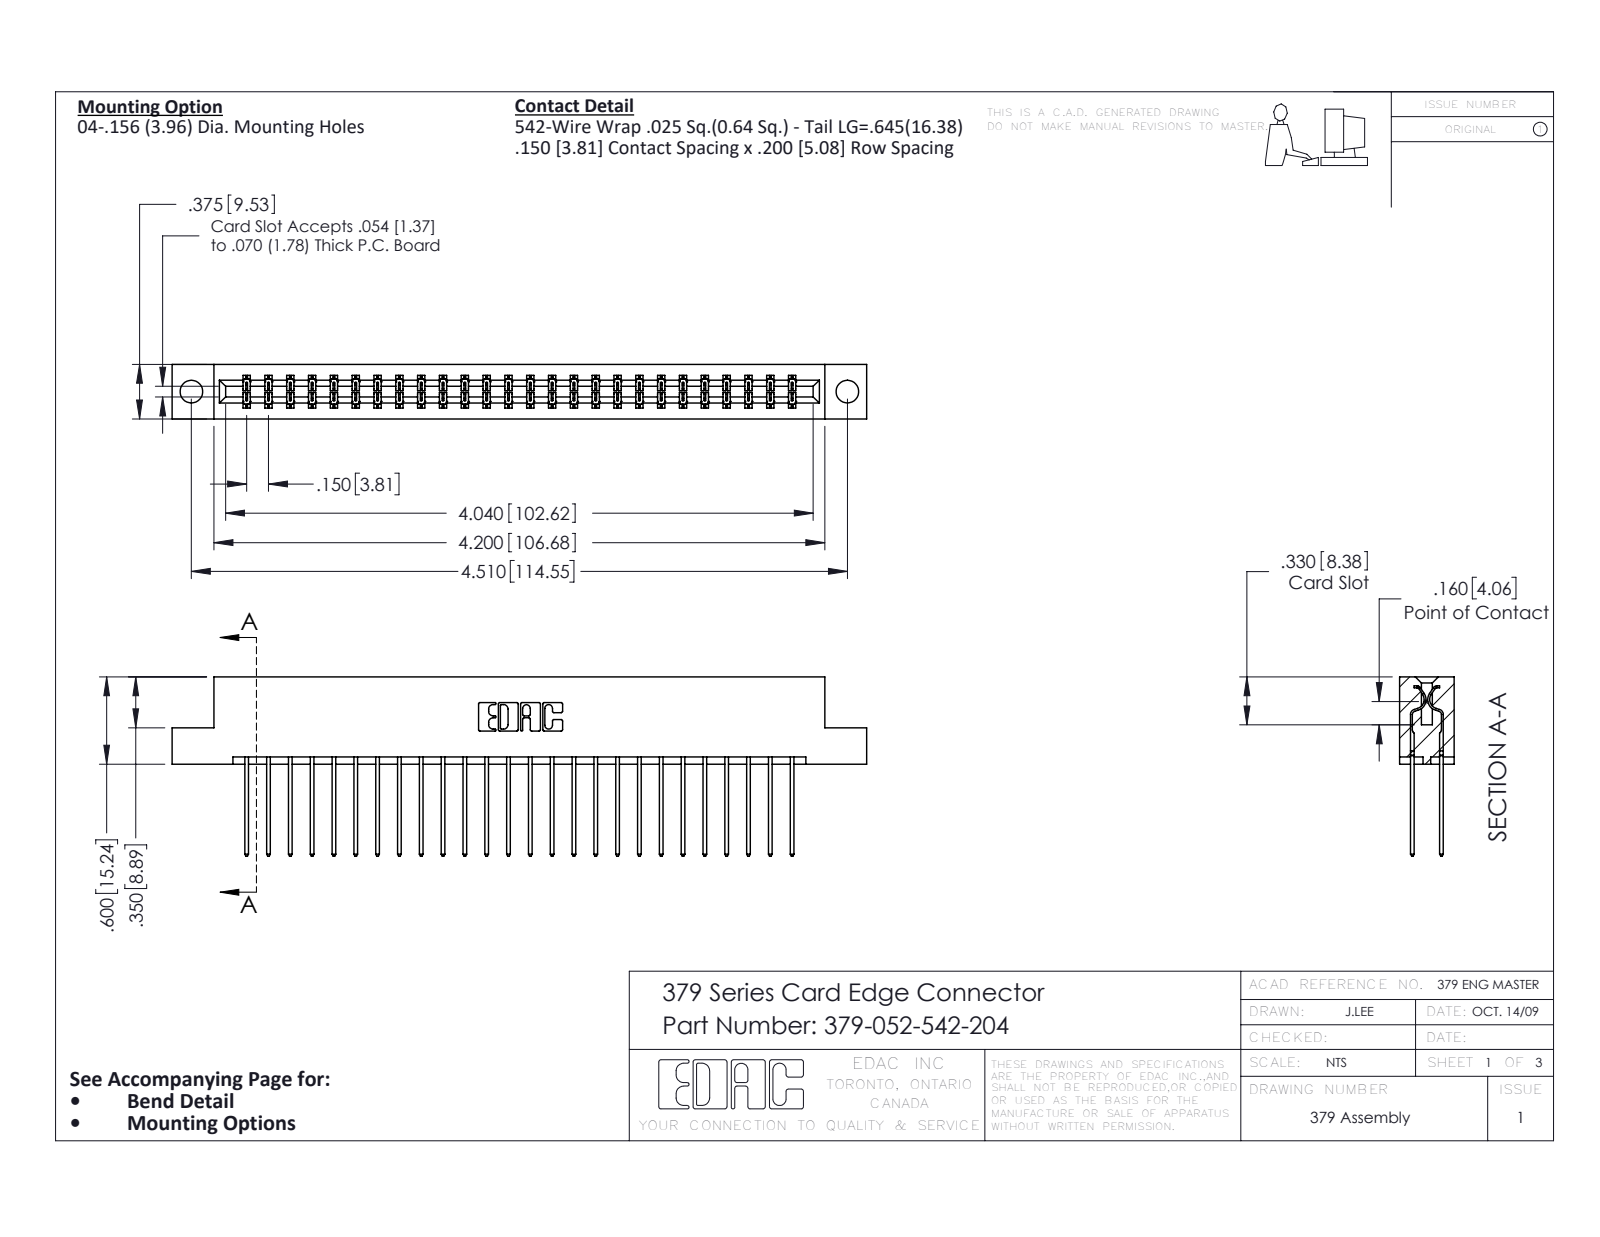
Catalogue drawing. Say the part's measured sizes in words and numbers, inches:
The part is named "345-292-001_345-293-142; 379-052-542-204; 379 Part_Flush - .156 Dia - TH". Its 3-D file was written by "SolidWorks 2016 (CONFIG_CONTROL_DESIGN)". It is 53 solids with 2818 faces: 1942 planar, 876 cylindrical and 0 other. Overall it measures 4.775 by 1.232 by 0.375 inches. Its volume is 0.786 cubic inches and its surface area 23.75 square inches. Round holes: 2 of diameter 0.156. Partial cylindrical surfaces (rounded edges, fillets, slot ends): 78 of radius 0.006, 52 of radius 0.01, 22 of radius 0.01, 6 of radius 0.007, 6 of radius 0.031, 3 of radius 0.026, 2 of radius 0.014, 2 of radius 0.022. The main face-to-face distances are 0.3, 0.075, 0.2, 0.375, 0.1, 0.275, 0.025, 0.076, 0.15, 0.225. The hole center spacings are 4.51.
